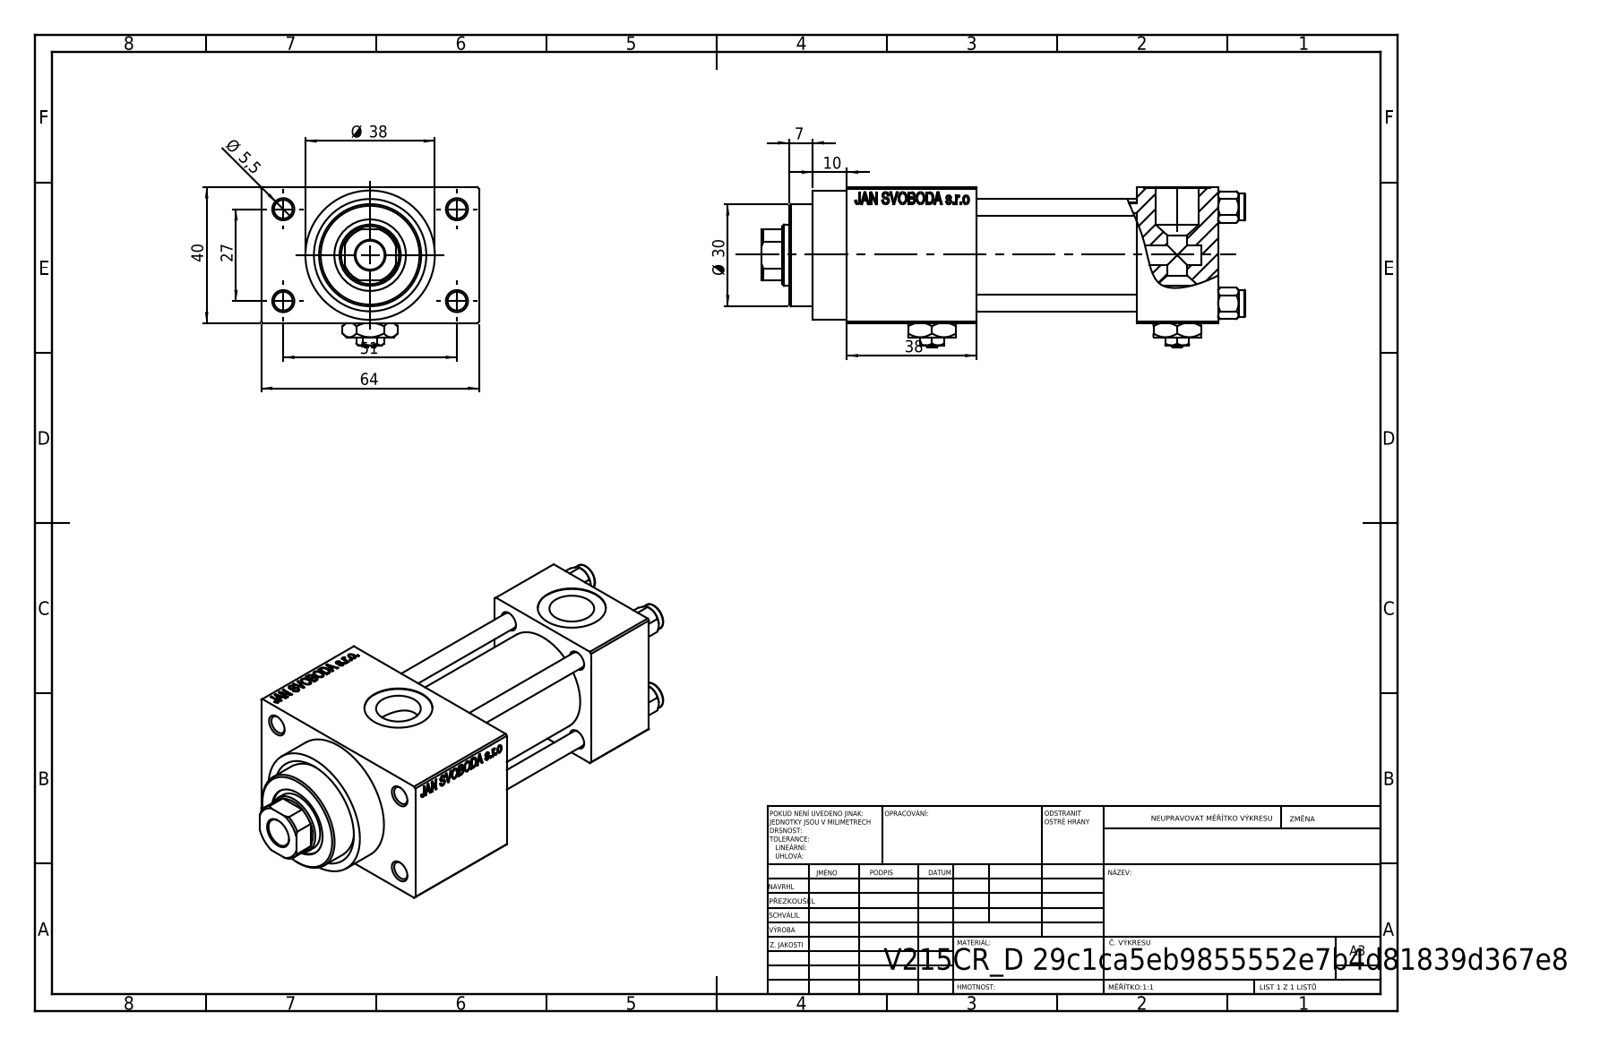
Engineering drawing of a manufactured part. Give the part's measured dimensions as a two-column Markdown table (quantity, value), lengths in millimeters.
| quantity | value |
| --- | --- |
| part name | V215CR_D_Body; V215CR_VCP_D; Zatka_pro_OIL_PORT; NUT_M5_D (+2 more) |
| STEP written by | SolidWorks 2019 (CONFIG_CONTROL_DESIGN) |
| units | millimeters |
| bodies | 13 solids, 1201 faces (541 planar, 98 cylindrical, 562 other) |
| overall size | 142 × 64 × 47 |
| volume | 179 653 mm³ |
| surface area | 65 784 mm² |
| round holes (diameter × count) | 5 × 4, 5.5 × 4, 20 × 3, 7 × 2, 13.16 × 2, 8.5 × 1, 18 × 1, 21 × 1, 25 × 1, 30 × 1 |
| round bosses / shafts (diameter × count) | 8 × 4, 38 × 1, 31 × 1 |
| partial cylindrical surfaces (radius × count) | 8.5 × 1 |
| main face-to-face distances | 40, 52, 12, 47, 24, 71, 64, 38, 85, 109 |
| hole center spacings | 11.37, 20.01, 28.3, 28.85, 29.89, 39.66, 48.34, 27 |
